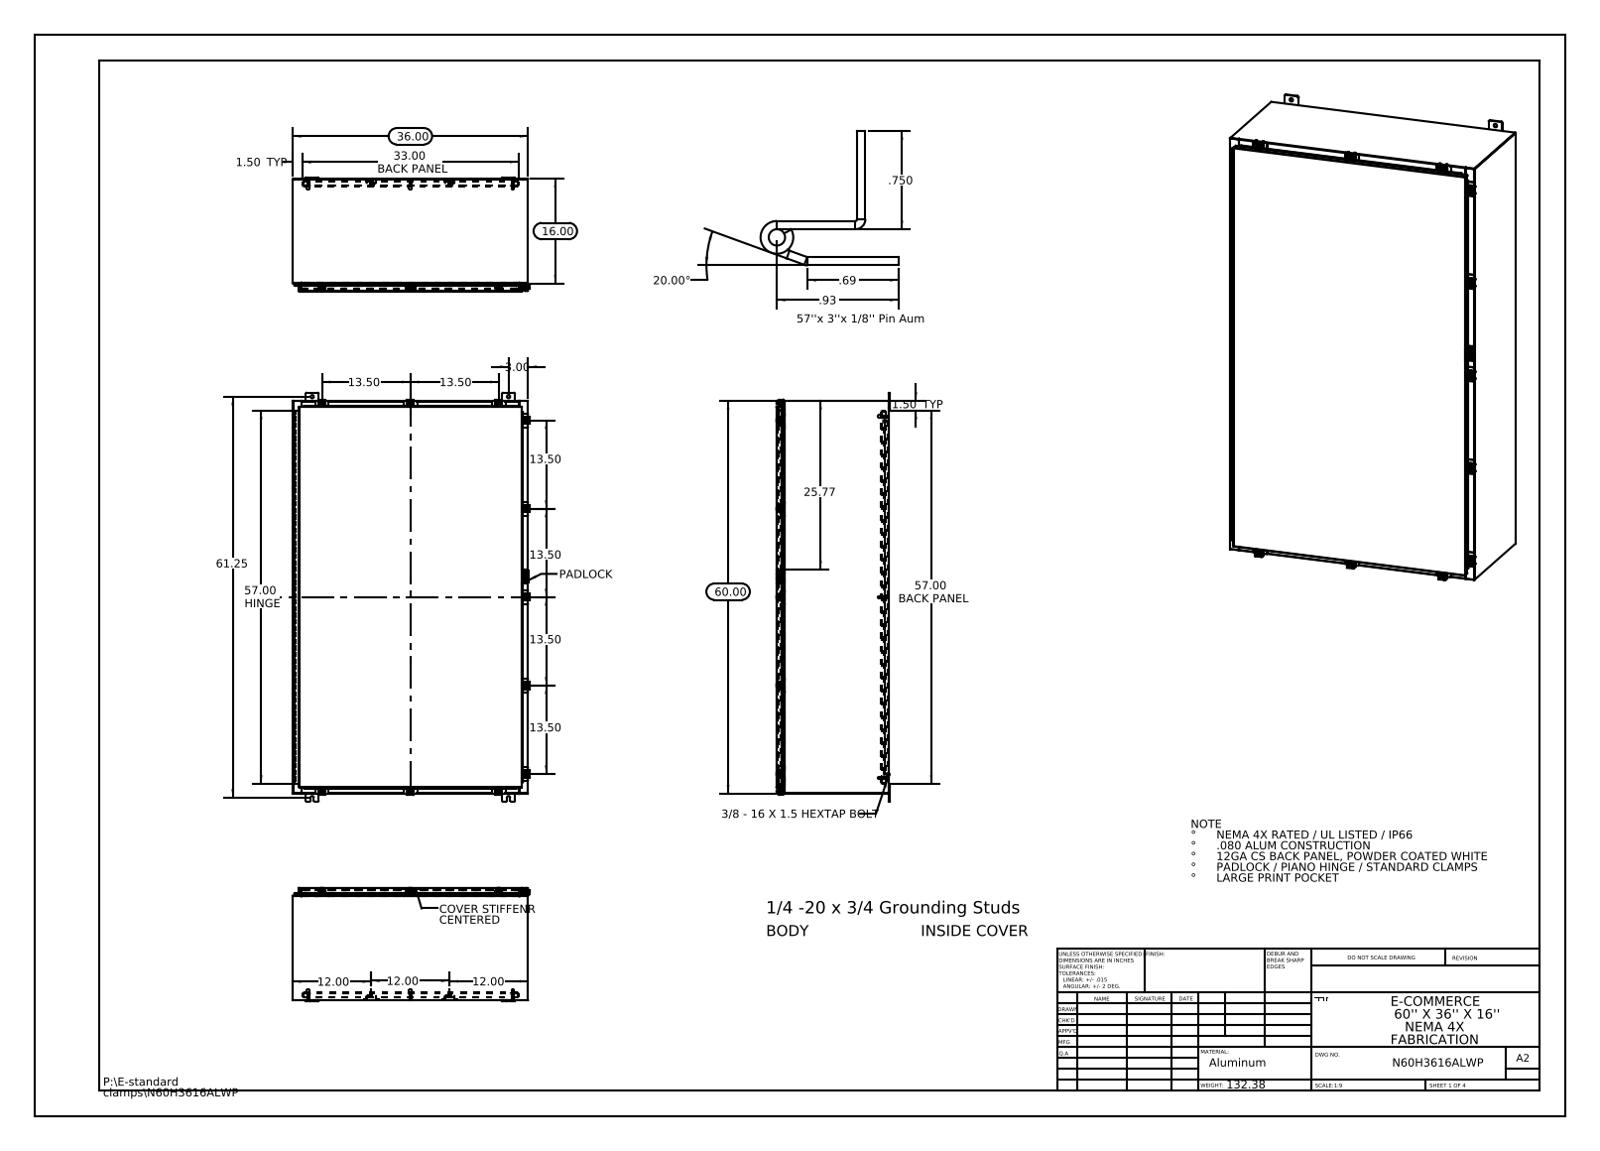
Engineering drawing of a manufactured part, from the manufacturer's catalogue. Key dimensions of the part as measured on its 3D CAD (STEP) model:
Part name (STEP PRODUCT): N60H3616ALWP Clamp Top; N60H3616ALWP Hinge Enclosure Side2; N60H3616ALWP 22104005_DEFAULT; N60H3616ALWP Standard Clamps (+8 more)
STEP written by: SolidWorks 2013 (CONFIG_CONTROL_DESIGN)
Units: inches
Bodies: 79 solids, 3408 faces (1766 planar, 1466 cylindrical, 176 other)
Overall size (bounding box): 62.5 × 36.211 × 17.389
Volume: 853.2 in³ · Surface area: 21 384 in²
Round holes (diameter × count): ⌀0.5 ×12, ⌀0.213 ×11, ⌀0.26 ×11, ⌀0.25 ×8, ⌀0.125 ×2, ⌀0.125 ×1
Round bosses / shafts (diameter × count): ⌀0.25 ×12, ⌀0.5 ×11, ⌀0.399 ×11, ⌀0.625 ×8, ⌀0.375 ×8, ⌀0.33 ×8
Partial cylindrical surfaces — rounded edges, fillets, slot ends (radius × count): R0.06 ×50, R0.013 ×39, R0.088 ×33, R0.19 ×24, R0.12 ×22, R0.141 ×22, R0.05 ×17, R0.08 ×16
Main face-to-face distances: 0.075, 17.126, 17.051, 0.104, 17.201, 35.925, 16.126, 1, 1.075, 16.051
Hole centre spacings: 13.5, 13.663, 2.225, 27, 27.625, 29.802, 41.709, 57.39
